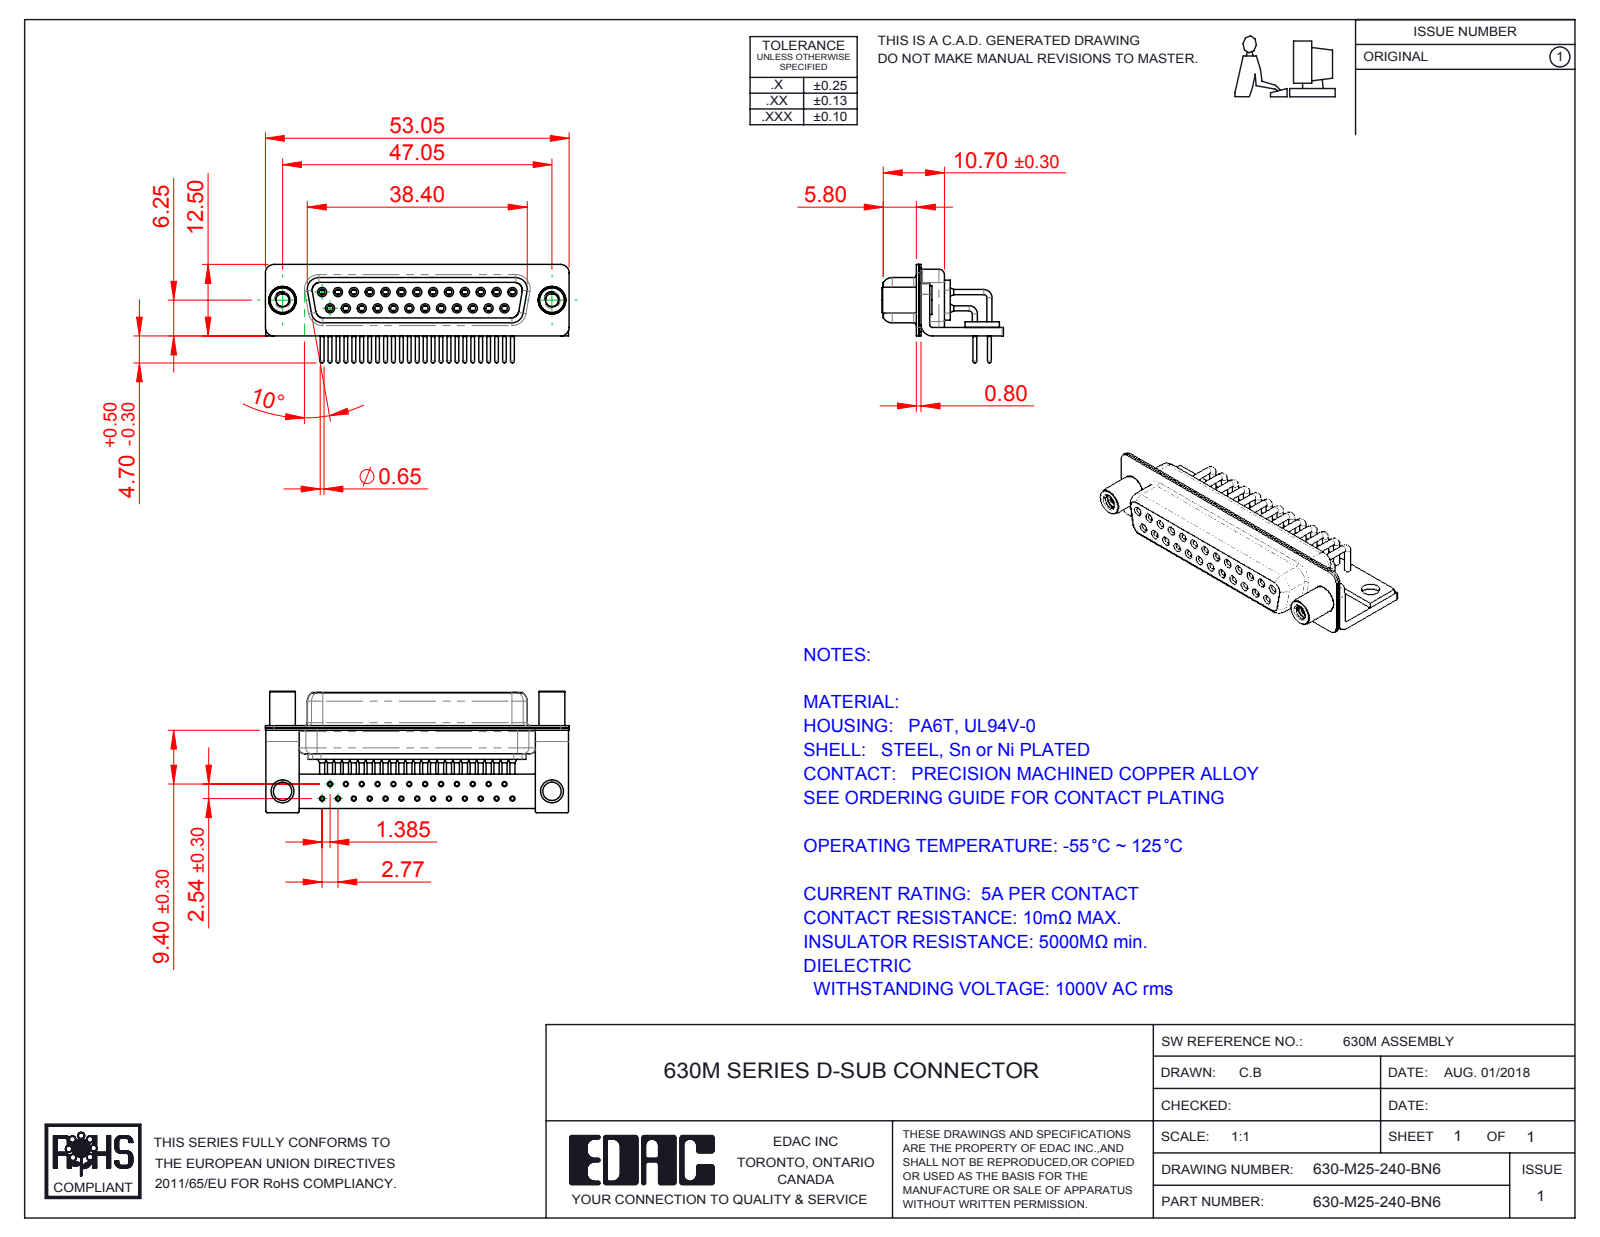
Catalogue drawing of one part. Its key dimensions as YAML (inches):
part_name: "630M Shell Rear_25 Contacts; 630M Contact Row 2; 630M Contact Row 1; 630-M25-240-BN6 (+5 more)"
step_written_by: "SolidWorks 2016 (CONFIG_CONTROL_DESIGN)"
units: inches
bodies: {solids: 33, faces: 1754, planar: 470, cylindrical: 826, other: 458}
overall_size: [2.089, 0.835, 0.677]
volume: 0.279
surface_area: 17.7
round_holes:
  - {diameter: 0.035, count: 25}
  - {diameter: 0.039, count: 25}
  - {diameter: 0.043, count: 25}
  - {diameter: 0.067, count: 25}
  - {diameter: 0.071, count: 25}
  - {diameter: 0.079, count: 25}
  - {diameter: 0.089, count: 2}
  - {diameter: 0.126, count: 2}
  - {diameter: 0.157, count: 2}
  - {diameter: 0.189, count: 2}
round_bosses_or_shafts:
  - {diameter: 0.063, count: 25}
  - {diameter: 0.059, count: 25}
  - {diameter: 0.035, count: 25}
  - {diameter: 0.026, count: 25}
  - {diameter: 0.197, count: 2}
  - {diameter: 0.193, count: 2}
  - {diameter: 0.177, count: 2}
partial_cylinders:
  - {radius: 0.01, count: 16}
  - {radius: 0.059, count: 16}
  - {radius: 0.079, count: 13}
  - {radius: 0.053, count: 10}
  - {radius: 0.063, count: 8}
  - {radius: 0.02, count: 5}
  - {radius: 0.024, count: 4}
  - {radius: 0.026, count: 4}
face_to_face_distances: [0.016, 0.091, 0.075, 0.057, 0.352, 0.033, 0.368, 0.031, 0.244, 0.039]
hole_center_spacings: [0.109, 0.218, 0.327, 0.436, 0.545, 0.124, 0.192, 0.654]
